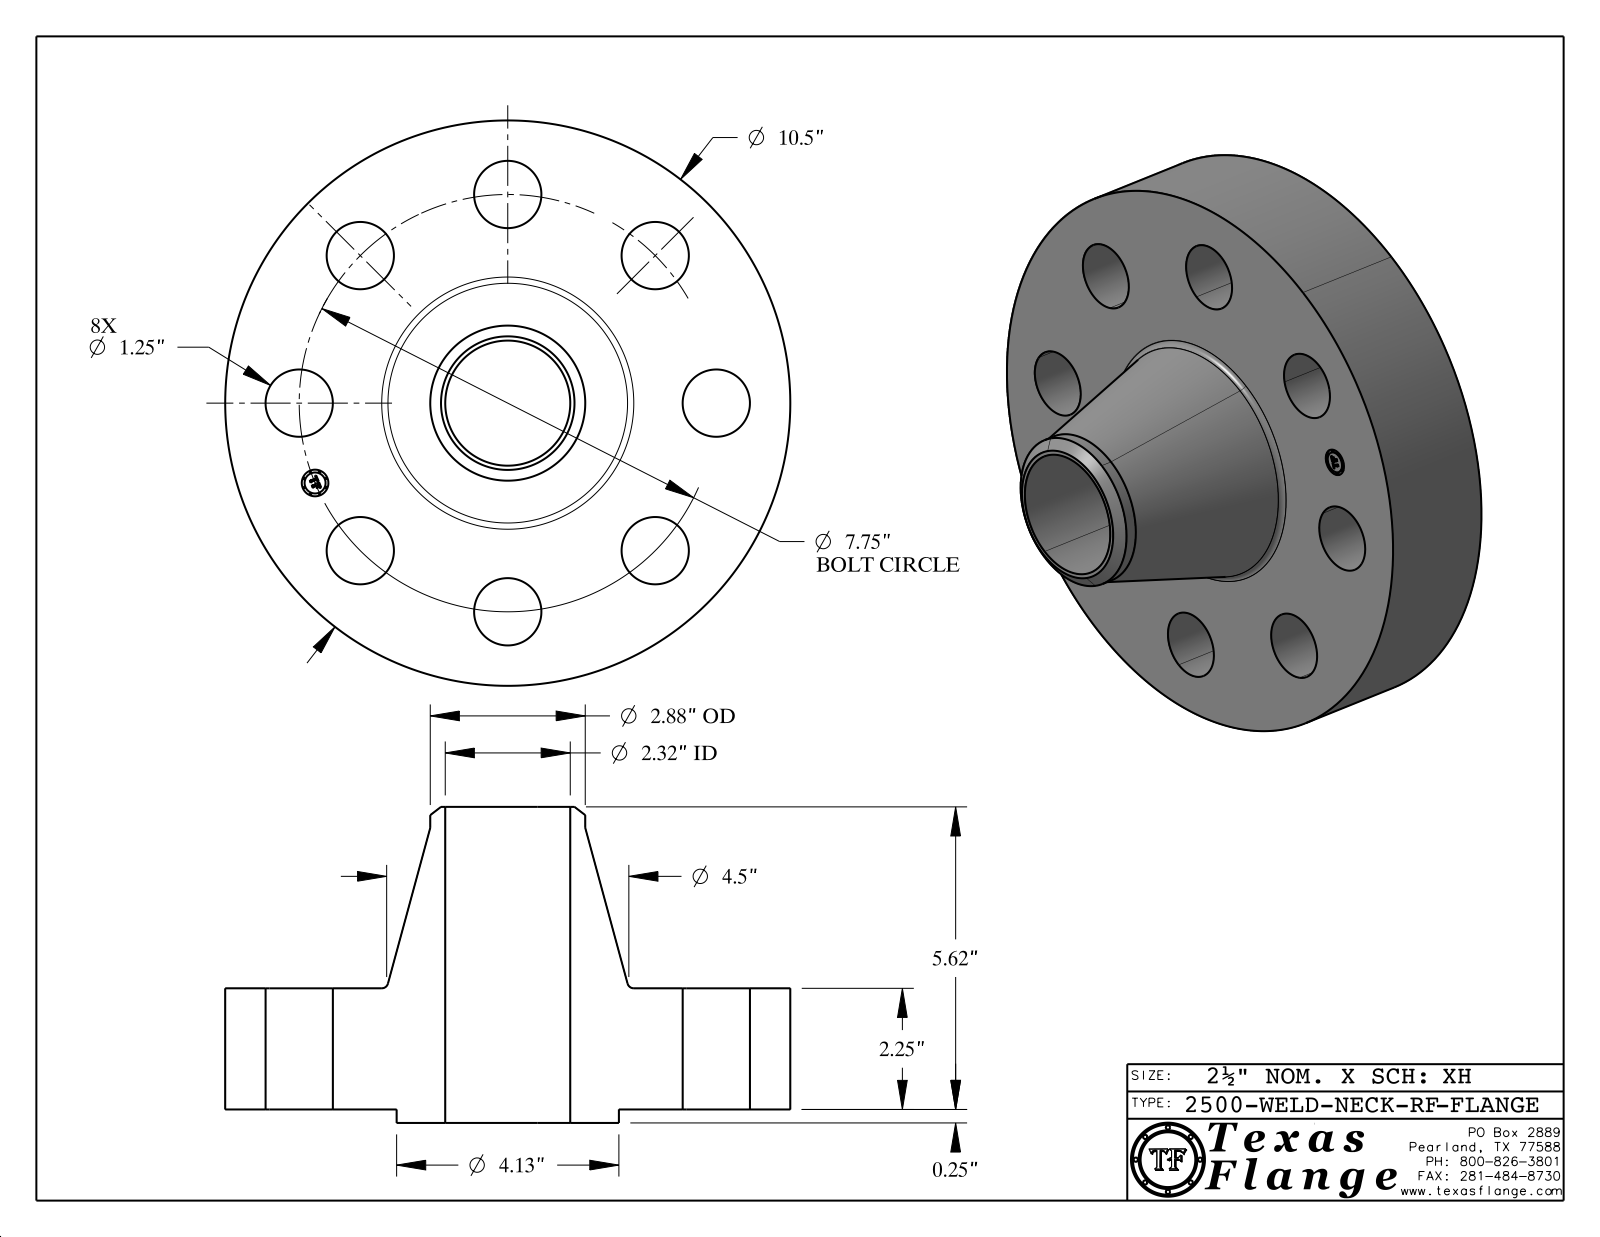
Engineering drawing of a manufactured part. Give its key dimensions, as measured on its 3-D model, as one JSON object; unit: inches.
{"part_name": "2500-WELD-NECK-RF", "step_written_by": "CATIA V5 STEP AP214 (AUTOMOTIVE_DESIGN)", "units": "inches", "bodies": {"solids": 1, "faces": 419, "planar": 369, "cylindrical": 44, "other": 6}, "overall_size": [10.5, 10.5, 5.87], "volume_in3": 186, "surface_area_in2": 364.8, "round_holes": [[1.25, 8], [0.495, 1], [2.323, 1]], "round_bosses_or_shafts": [[0.03, 8], [10.5, 1], [4.13, 1], [2.88, 1], [0.39, 1]], "face_to_face_distances": [2.25, 0.25, 2.5, 5.87, 5.62, 3.37, 2.485, 2.235, 0.015, 3.385], "hole_center_spacings": [2.966, 3.875, 5.48, 7.16, 7.75, 7.601, 1.512, 1.512]}
